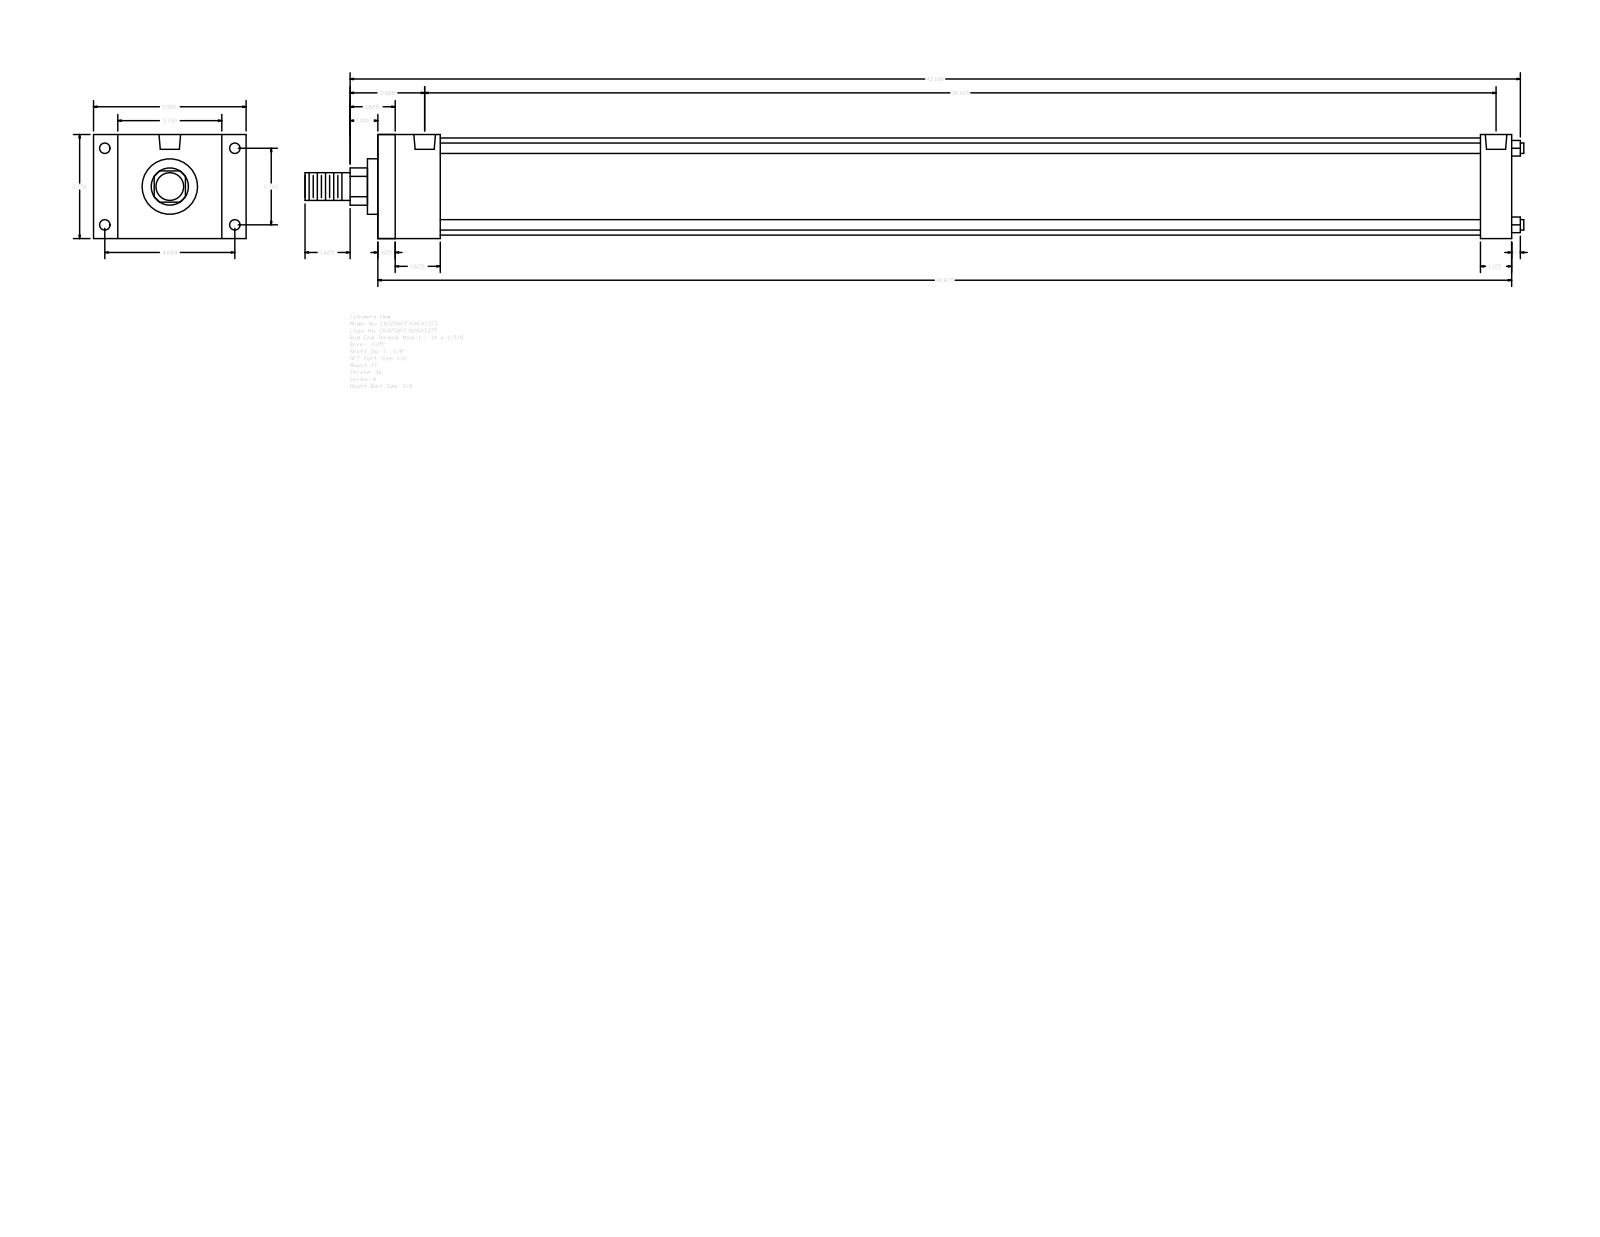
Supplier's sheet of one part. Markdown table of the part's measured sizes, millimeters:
| quantity | value |
| --- | --- |
| part name | A_FF__0325_1.375 |
| STEP written by | GSSL Pune (CONFIG_CONTROL_DESIGN) |
| units | millimeters |
| bodies | 0 solids, 92 faces (64 planar, 28 cylindrical, 0 other) |
| overall size | 1116.01 × 139.7 × 95.25 |
| round holes (diameter × count) | 8.73 × 4, 9.53 × 4, 19.77 × 2 |
| round bosses / shafts (diameter × count) | 9.53 × 4, 88.9 × 1, 50.8 × 1, 34.92 × 1, 25.4 × 1 |
| partial cylindrical surfaces (radius × count) | 17.06 × 1 |
| main face-to-face distances | 95.24, 1038.22, 1022.35, 15.87, 57.15, 22.23, 117.47, 28.57, 1009.65, 41.28 |
| hole center spacings | 3.18, 70.1, 119.06, 138.16, 974.72, 977.9, 981.08 |
